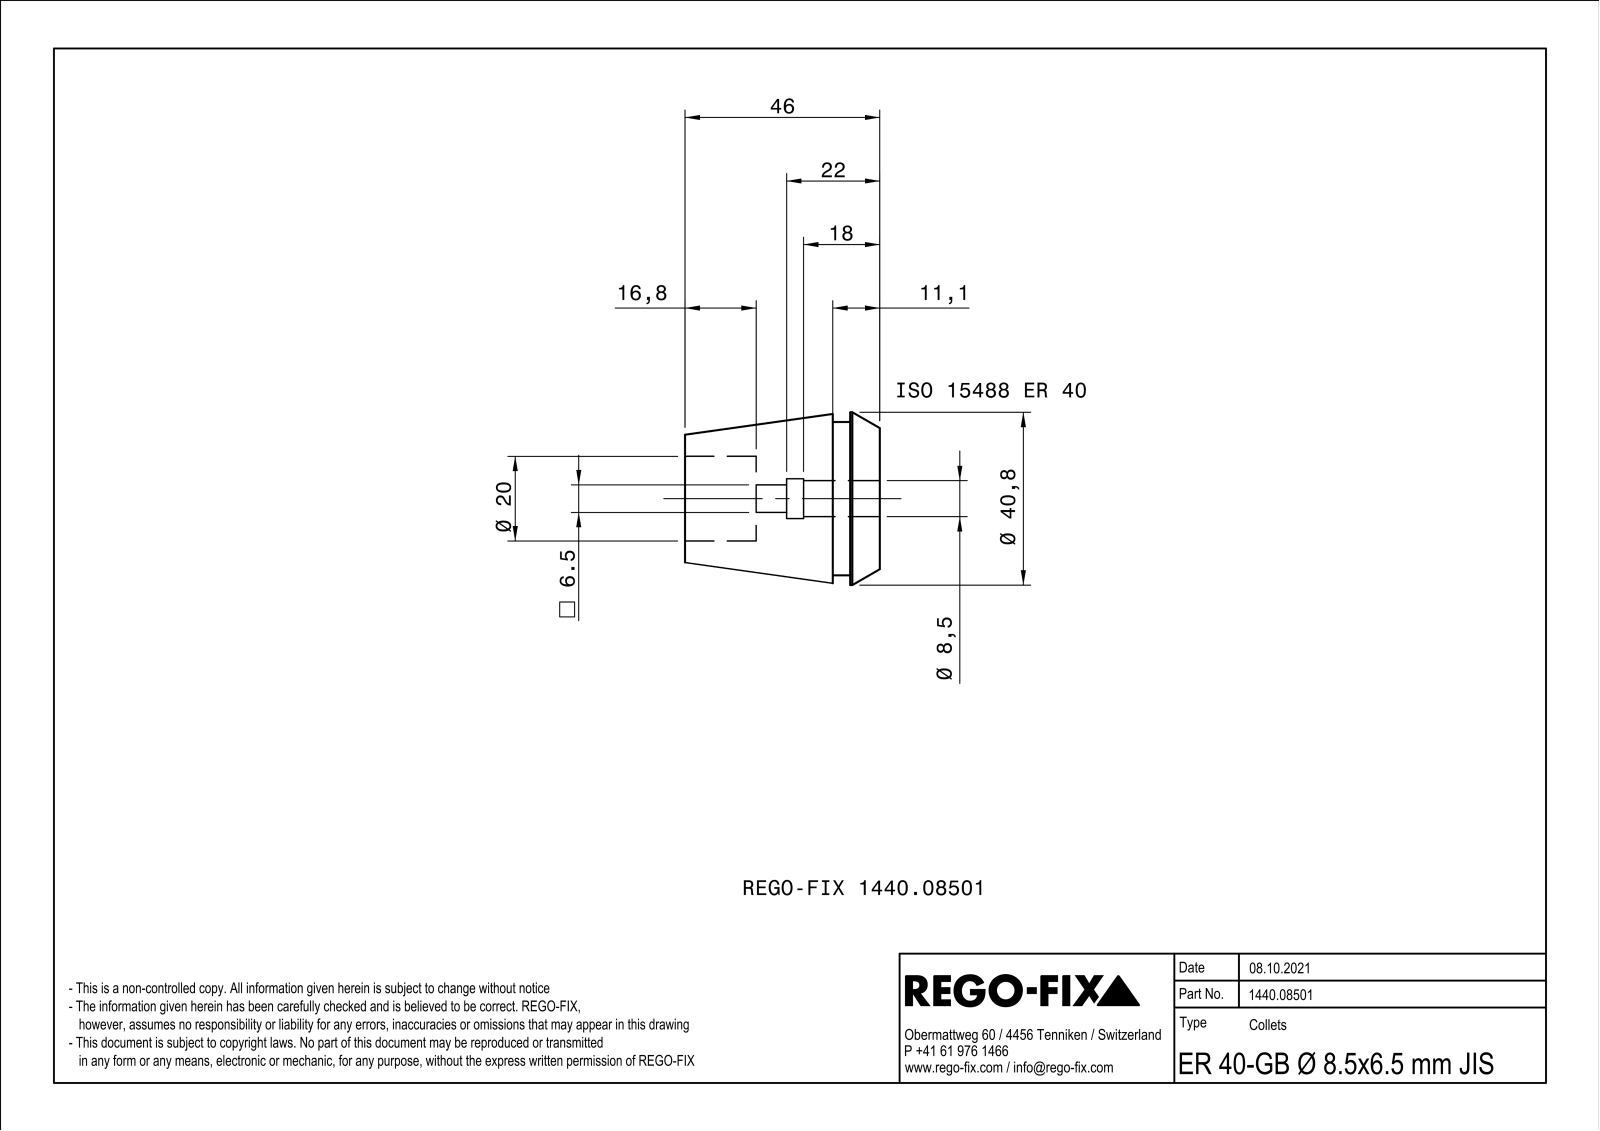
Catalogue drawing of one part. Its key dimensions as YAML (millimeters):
part_name: "NOCUT"
step_written_by: "SIEMENS PLM Software Solid Edge ST10 (AUTOMOTIVE_DESIGN)"
units: millimeters
bodies: {solids: 1, faces: 160, planar: 68, cylindrical: 32, other: 60}
overall_size: [46, 40.79, 40.79]
volume: 35241
surface_area: 15743
round_holes:
  - {diameter: 8.5, count: 1}
  - {diameter: 20, count: 1}
round_bosses_or_shafts:
  - {diameter: 40.8, count: 1}
  - {diameter: 36.2, count: 1}
partial_cylinders:
  - {radius: 3.85, count: 1}
  - {radius: 4.7, count: 1}
face_to_face_distances: [1, 46, 7, 39, 11.1, 4.1, 34.9, 29.2, 22.2, 18.1]
